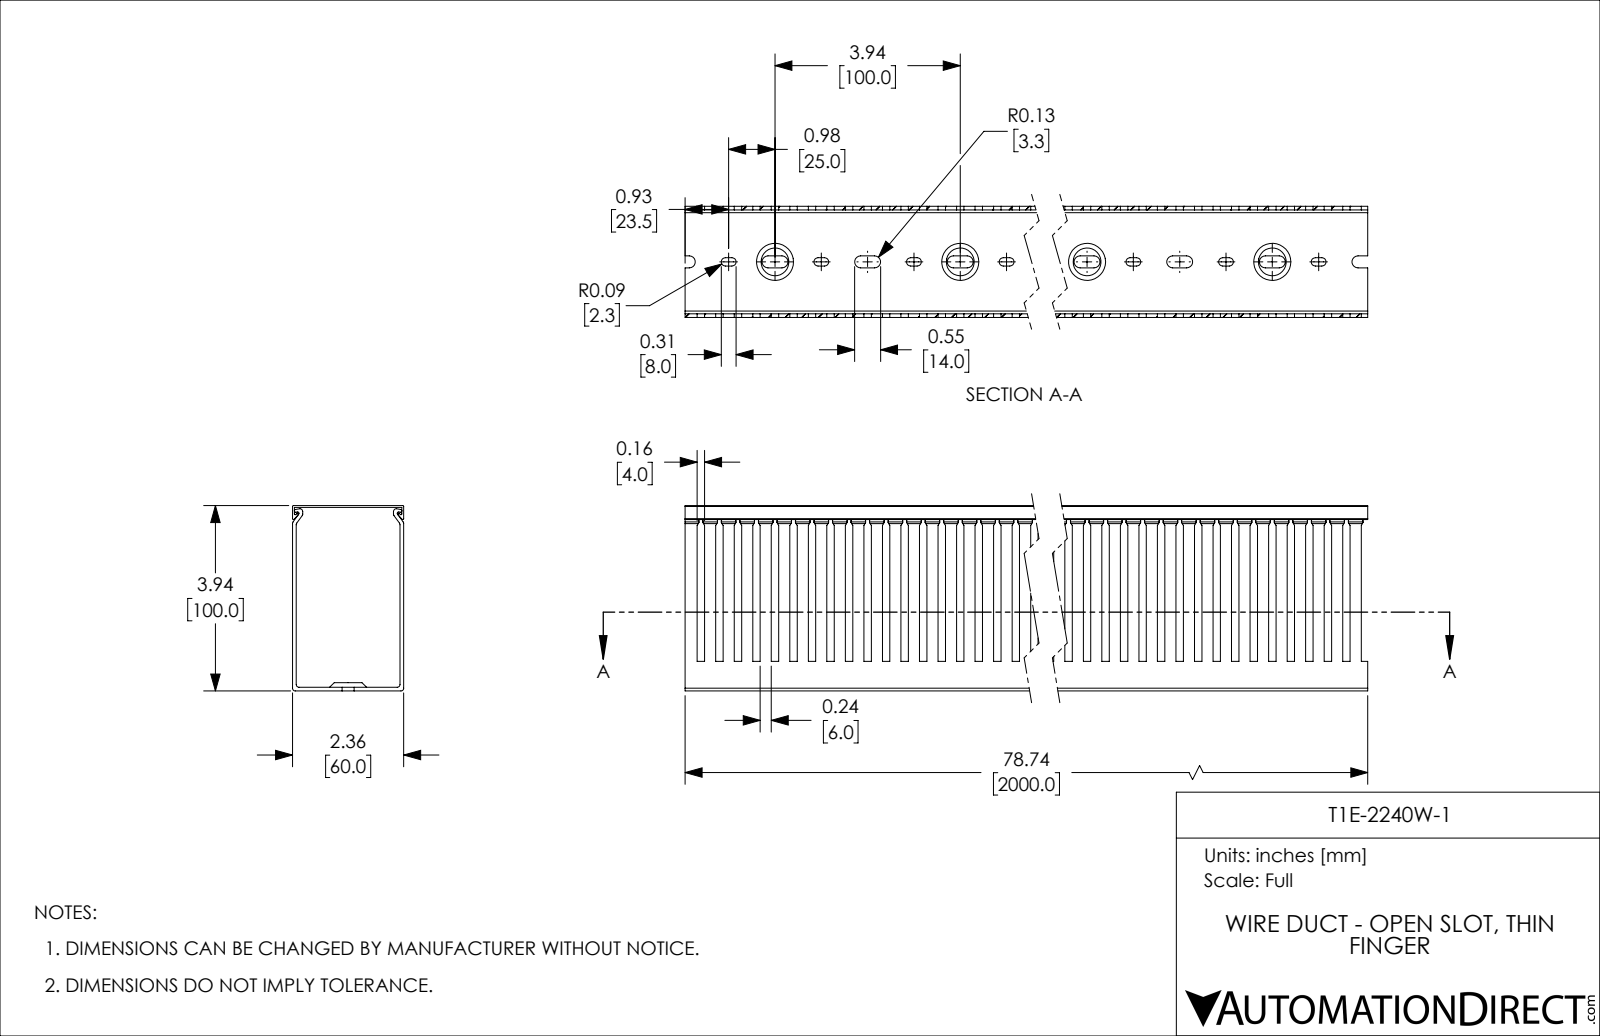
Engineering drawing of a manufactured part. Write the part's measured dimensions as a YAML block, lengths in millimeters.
part_name: "T1E-2240W-1"
step_written_by: "SolidWorks 2021 (CONFIG_CONTROL_DESIGN)"
units: millimeters
bodies: {solids: 2, faces: 1005, planar: 534, cylindrical: 431, other: 40}
overall_size: [2000, 100, 60]
volume: 1176000
surface_area: 1336000
partial_cylinders:
  - {radius: 2.25, count: 80}
  - {radius: 3.25, count: 80}
  - {radius: 1.5, count: 12}
  - {radius: 0.5, count: 8}
  - {radius: 0.75, count: 6}
face_to_face_distances: [2, 58, 60, 56, 1, 99, 100, 97, 98, 59]
